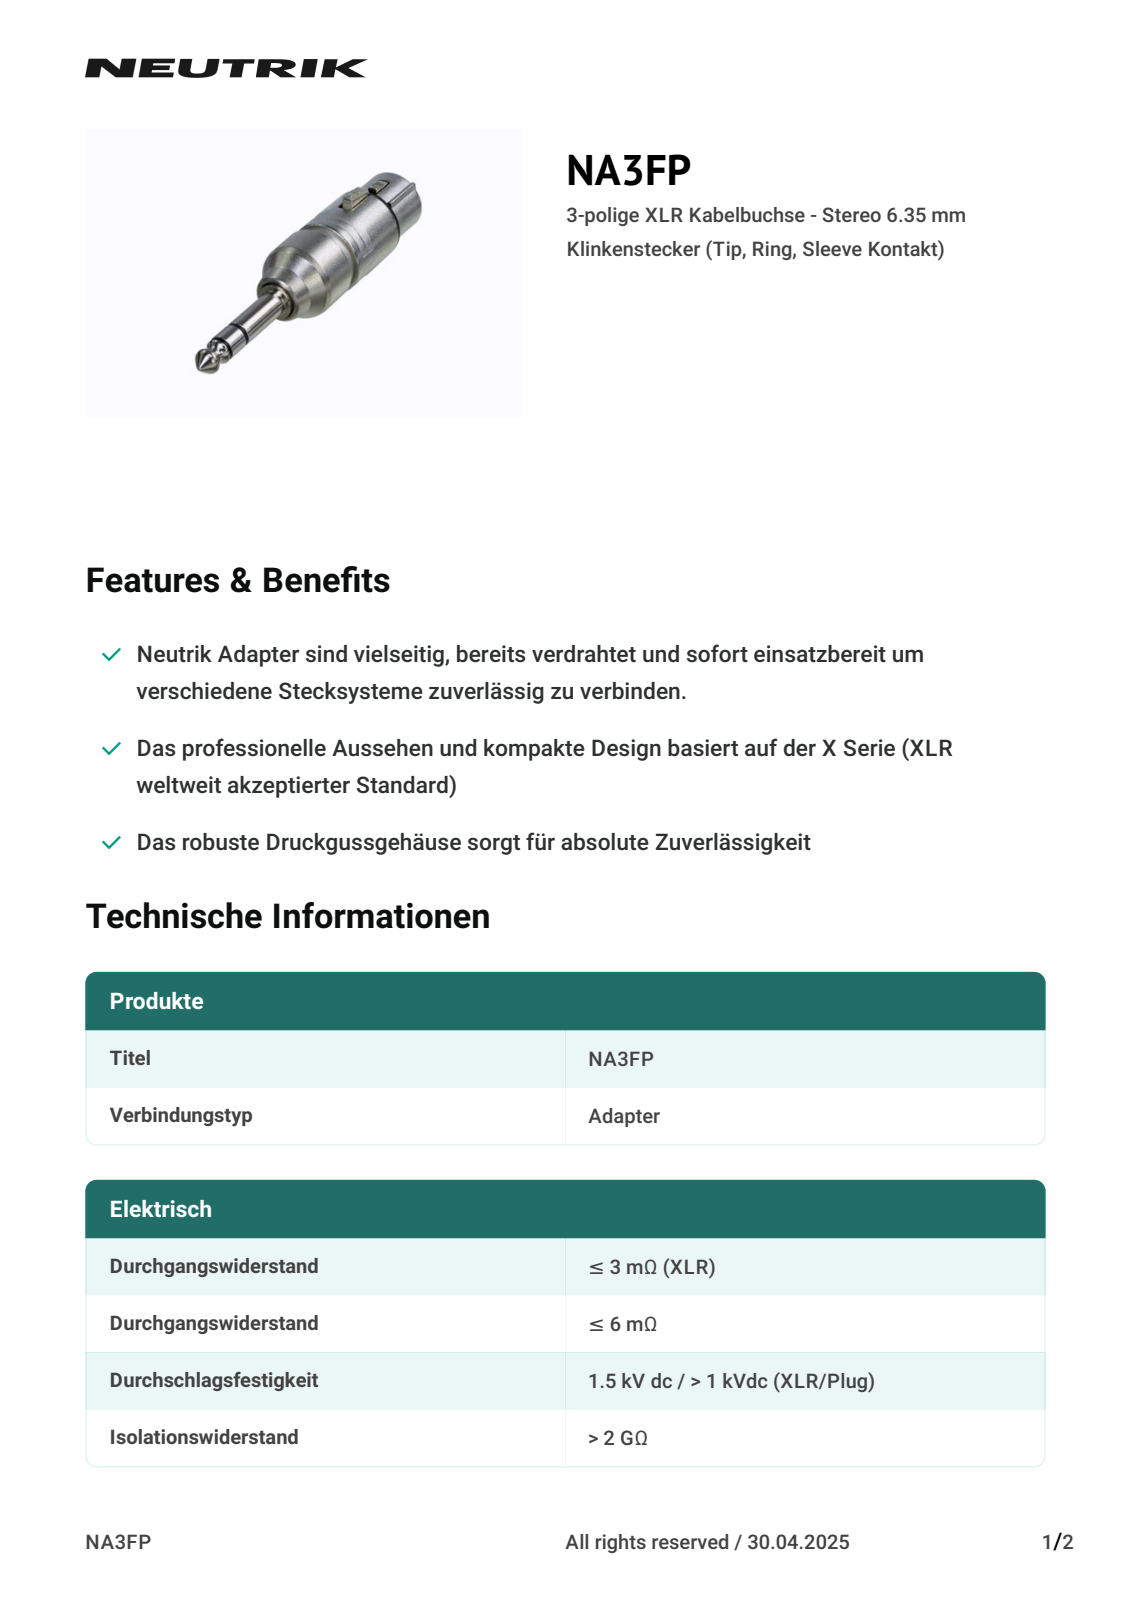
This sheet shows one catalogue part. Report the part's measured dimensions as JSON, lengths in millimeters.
{"part_name": "NA3FP", "step_written_by": "CREO PARAMETRIC BY PTC INC, 2018360 (CONFIG_CONTROL_DESIGN)", "units": "millimeters", "bodies": {"solids": 1, "faces": 706, "planar": 536, "cylindrical": 100, "other": 70}, "overall_size": [82.69, 22.13, 19], "volume_mm3": 13220, "surface_area_mm2": 4311, "round_holes": [[2.5, 3], [3.35, 1], [5, 1], [9.1, 1], [13, 1]], "round_bosses_or_shafts": [[19, 1], [18.8, 1], [17, 1], [15.75, 1], [15.15, 1], [12.9, 1], [8.95, 1], [6.29, 1]], "partial_cylinders_radius": [[0.25, 9], [0.2, 5], [0.75, 3], [0.8, 3], [0.4, 2], [0.21, 1], [0.26, 1], [0.3, 1]], "face_to_face_distances": [32.8, 33, 3, 13.9, 1.1, 51, 50.8, 18, 1.6, 1.8], "hole_center_spacings": [4.05, 5.66, 3.95, 8.1]}
